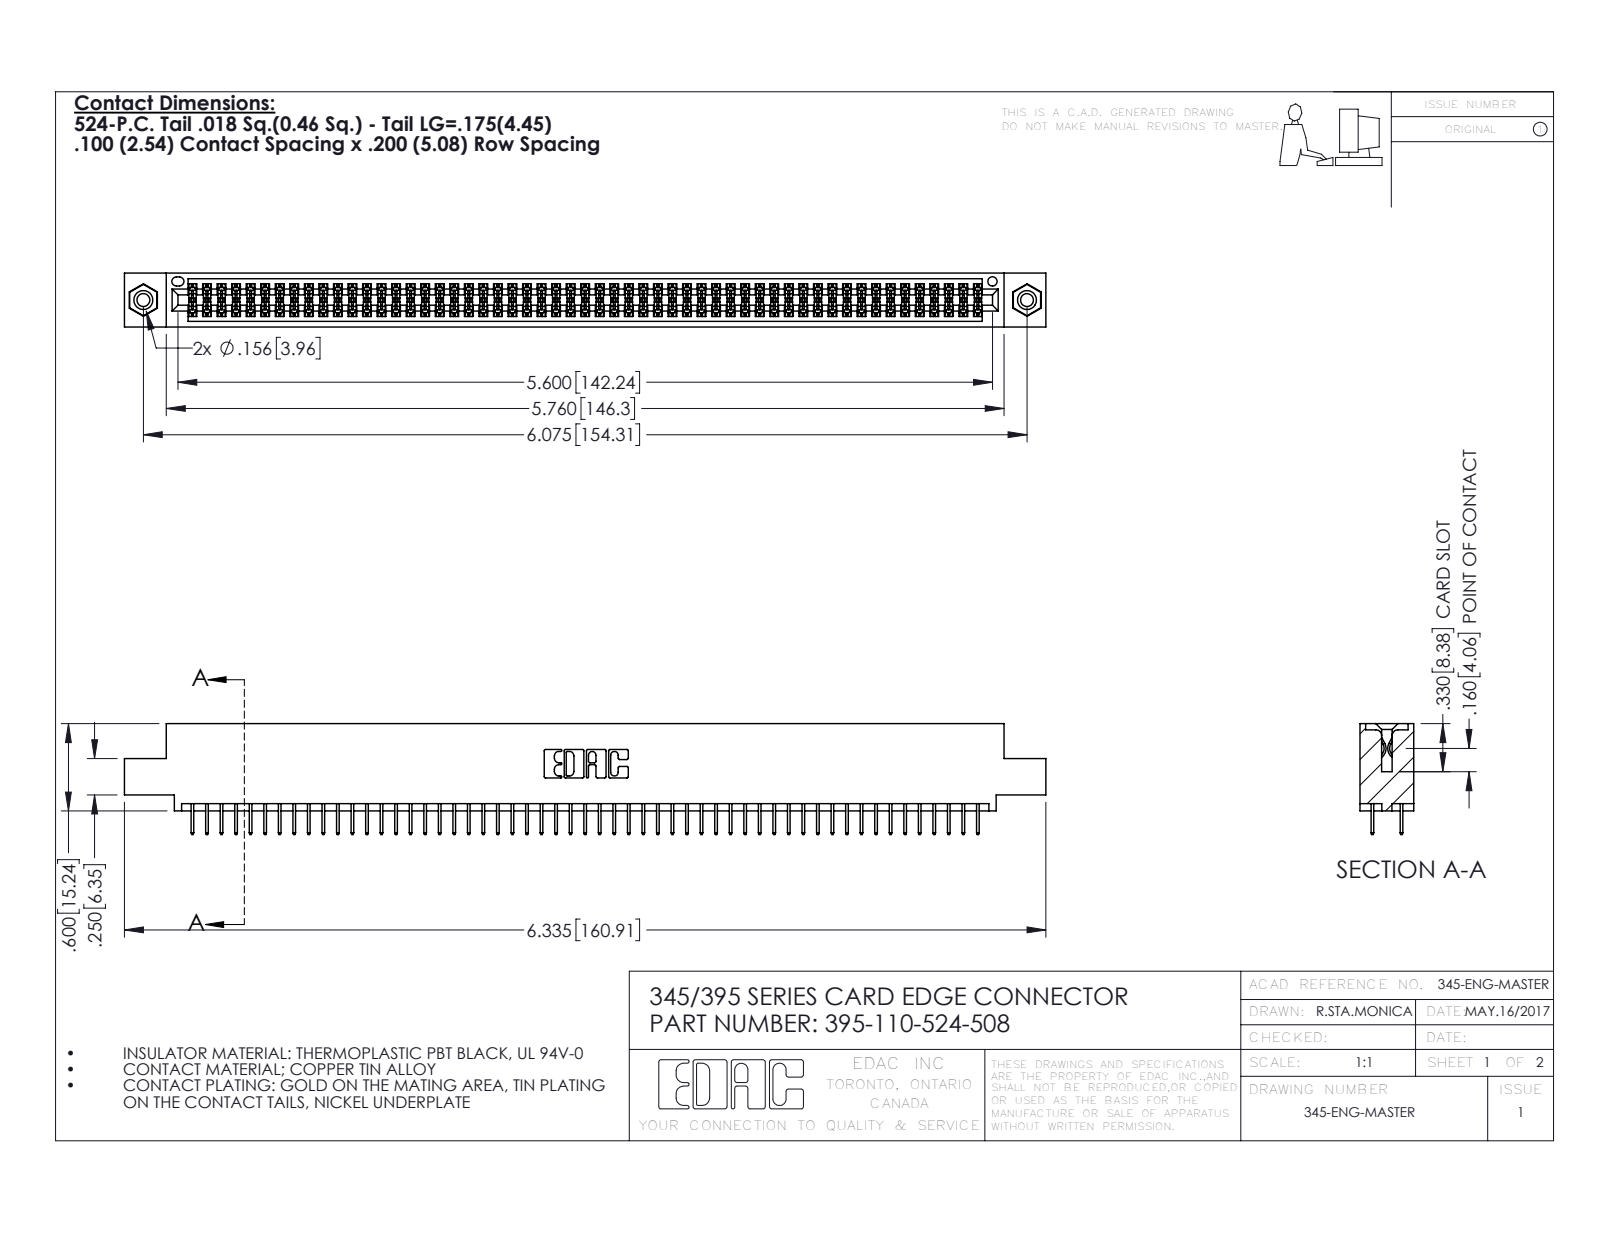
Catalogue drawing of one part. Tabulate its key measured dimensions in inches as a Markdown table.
| quantity | value |
| --- | --- |
| part name | 345-250-001_345-250-003-102; 345-292-001_345-293-124; 395-110-524-508; 345 Part_0.110 Offset - 0.156 Dia-TI |
| STEP written by | SolidWorks 2016 (CONFIG_CONTROL_DESIGN) |
| units | inches |
| bodies | 113 solids, 6130 faces (4406 planar, 1708 cylindrical, 16 other) |
| overall size | 6.335 × 0.762 × 0.37 |
| volume | 0.946 in³ |
| surface area | 35.4 in² |
| round holes (diameter × count) | 0.089 × 2, 0.125 × 2, 0.156 × 2, 0.064 × 1 |
| round bosses / shafts (diameter × count) | 0.155 × 2 |
| partial cylindrical surfaces (radius × count) | 0.006 × 165, 0.01 × 22, 0.007 × 6, 0.031 × 6, 0.026 × 3, 0.014 × 2, 0.019 × 2, 0.022 × 2 |
| main face-to-face distances | 0.072, 0.298, 0.2, 0.37, 0.098, 0.272, 0.025, 0.225, 0.072, 0.175 |
| hole center spacings | 0.27, 5.839, 6.075 |
